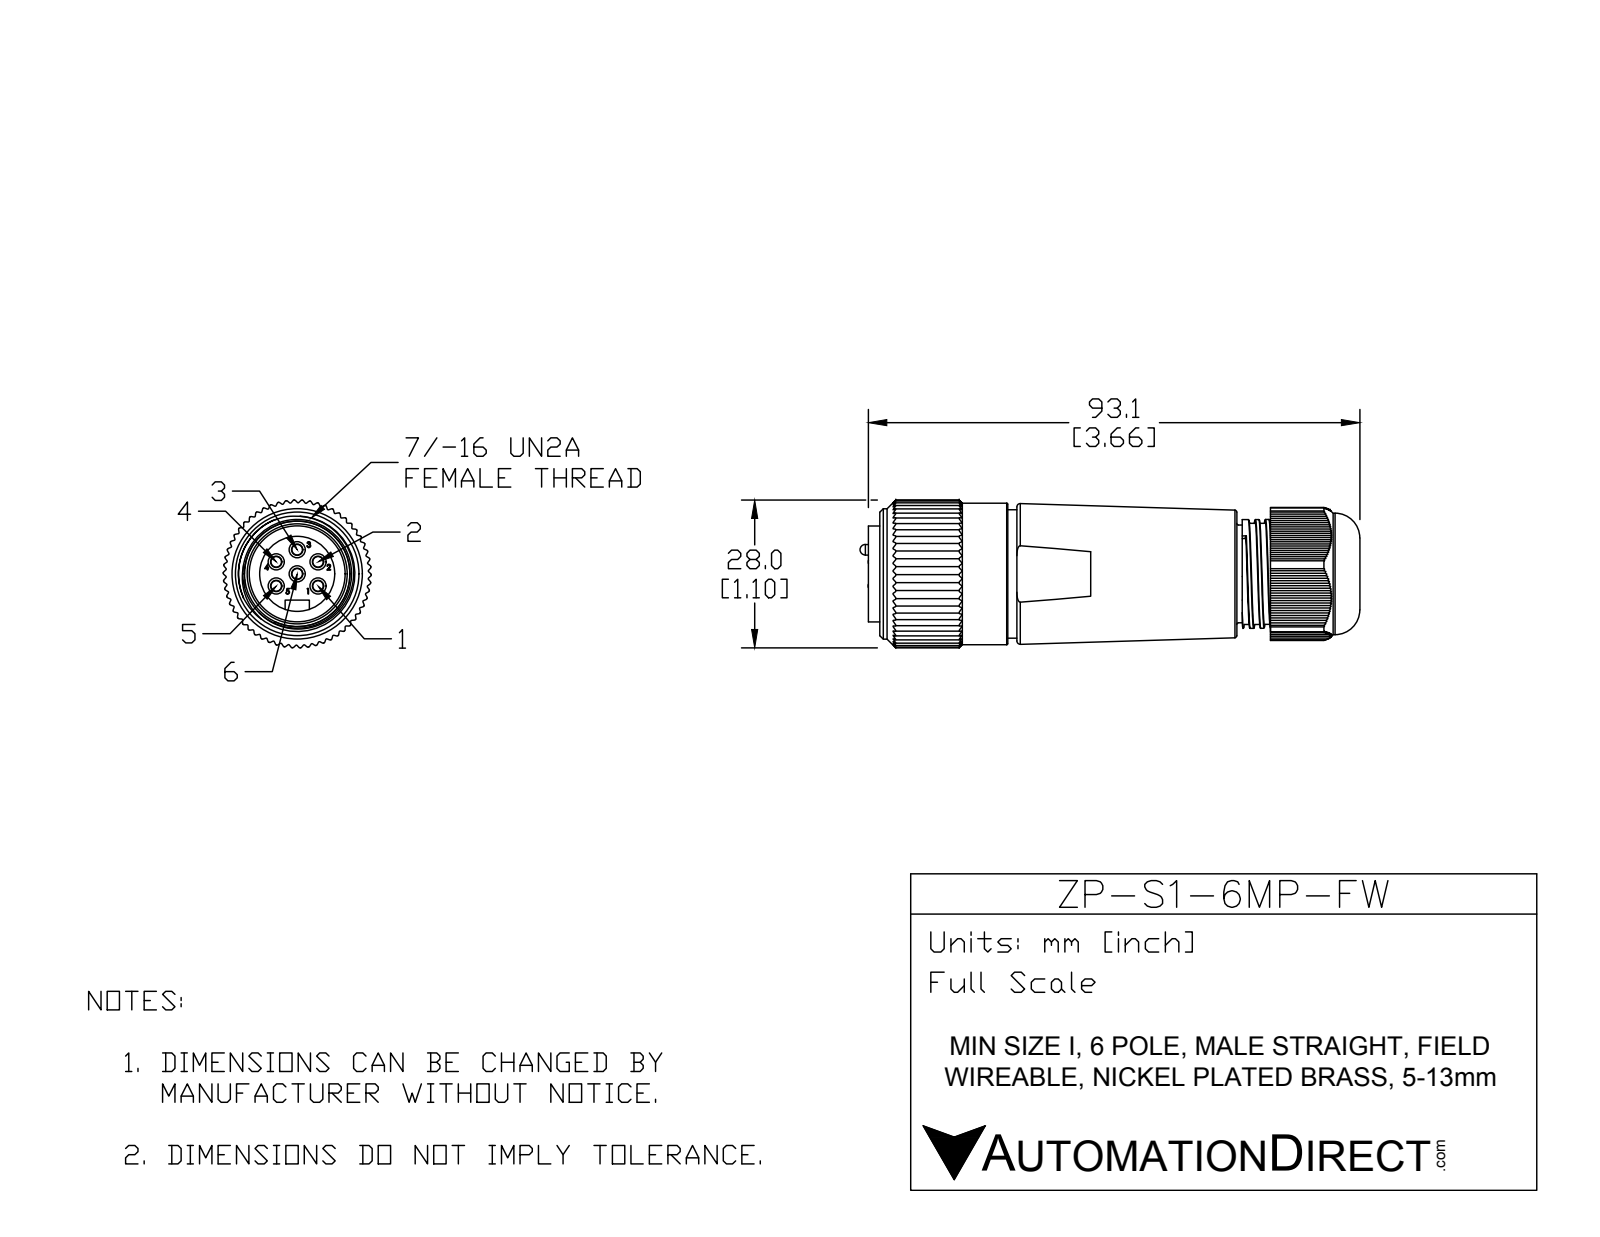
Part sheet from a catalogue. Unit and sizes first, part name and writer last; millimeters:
Units: millimetres
Overall size (bounding box): 95.14 × 27.99 × 27.98
Round holes (diameter × count): ⌀3.56 ×1, ⌀13.46 ×1, ⌀14.22 ×1, ⌀20.58 ×1, ⌀21.57 ×1, ⌀24.2 ×1, ⌀25.4 ×1
Round bosses / shafts (diameter × count): ⌀3.15 ×6, ⌀2 ×6, ⌀26.8 ×1, ⌀24.68 ×1, ⌀24.3 ×1, ⌀22.99 ×1, ⌀20.6 ×1, ⌀18.14 ×1
Partial cylindrical surfaces — rounded edges, fillets, slot ends (radius × count): R0.25 ×165, R2.29 ×1, R13.23 ×1, R14 ×1
Main face-to-face distances: 69.12, 1.06, 0.35, 0.71, 70.28, 6.35, 8.79, 60.33, 1.41, 2.12
Volume: 41 962 mm³ · Surface area: 15 119 mm²
Bodies: 10 solids, 874 faces (468 planar, 318 cylindrical, 88 other)
Part name (STEP PRODUCT): ZP-S1-6MP-FW
STEP written by: SolidWorks 2015 (AUTOMOTIVE_DESIGN)
